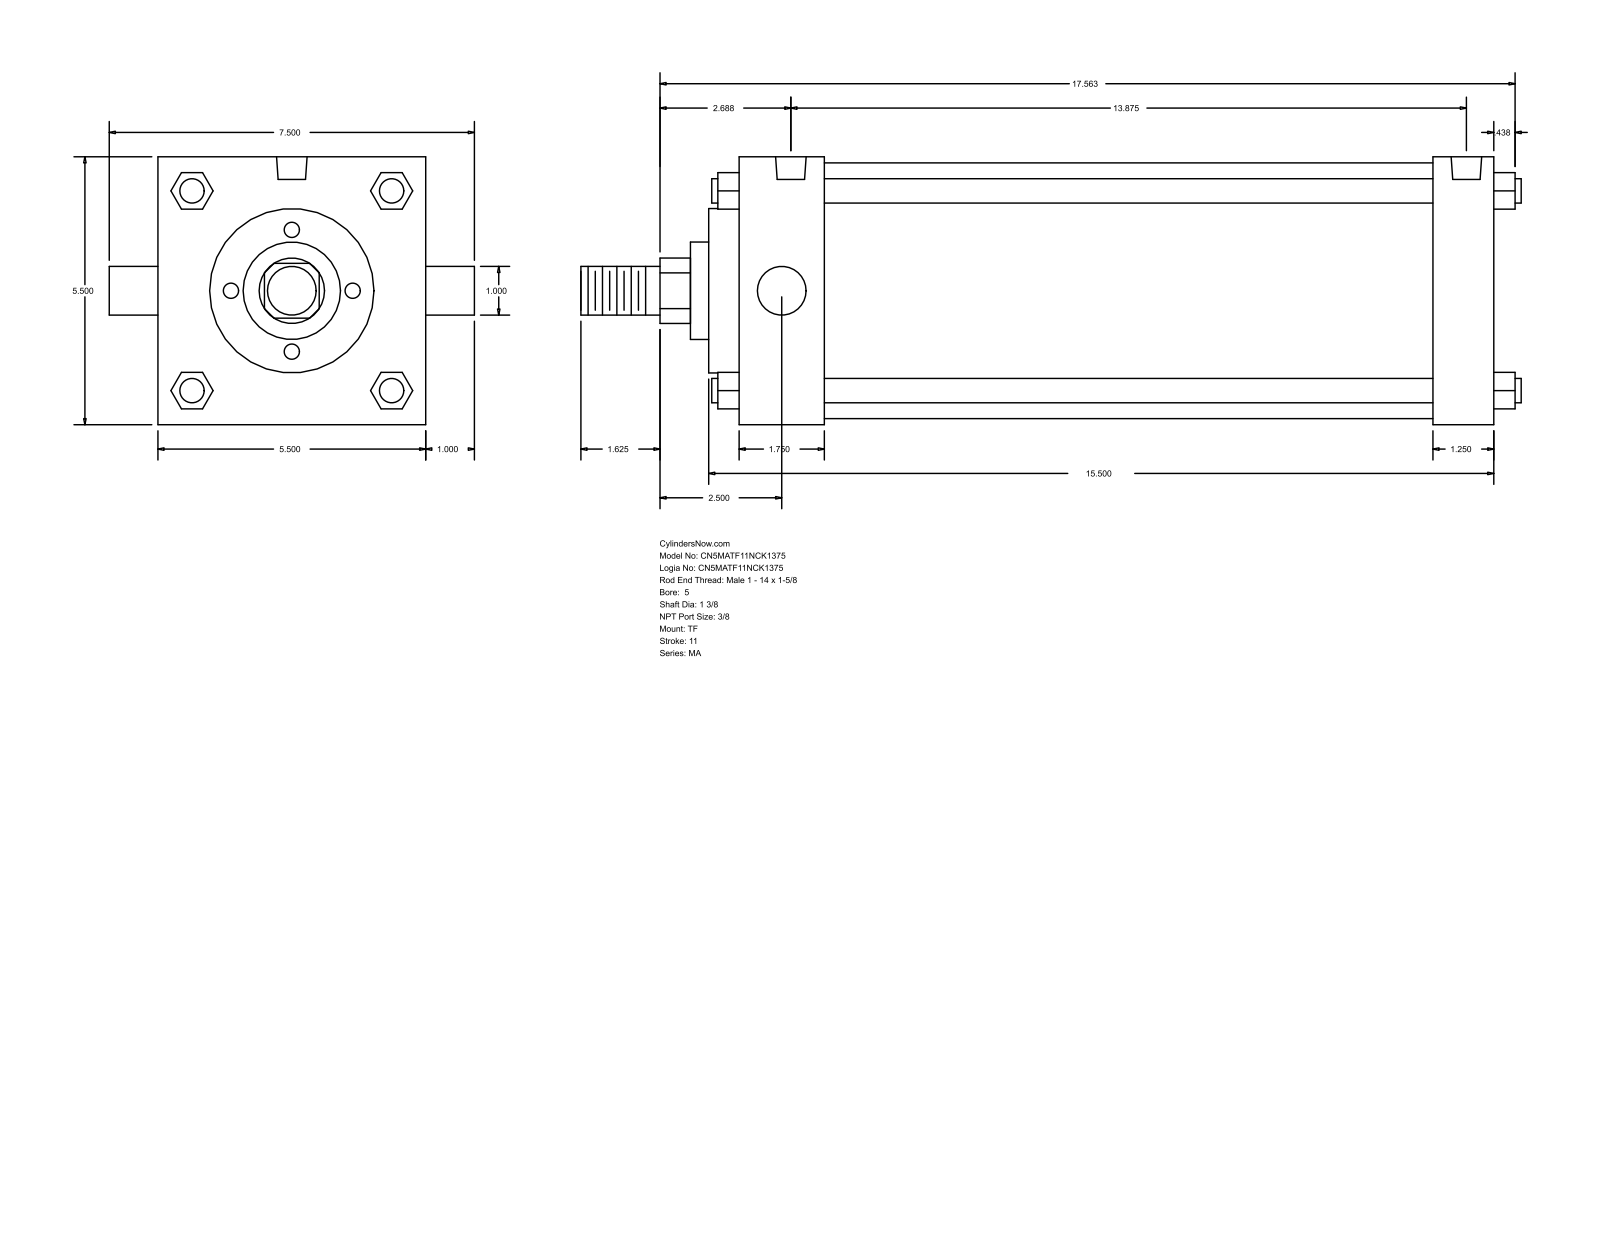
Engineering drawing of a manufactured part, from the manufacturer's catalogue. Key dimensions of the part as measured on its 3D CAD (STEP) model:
Part name (STEP PRODUCT): MA_TF__0500_1.375
STEP written by: GSSL Pune (CONFIG_CONTROL_DESIGN)
Units: millimetres
Bodies: 0 solids, 122 faces (93 planar, 29 cylindrical, 0 other)
Overall size (bounding box): 490.54 × 190.5 × 139.7
Round holes (diameter × count): ⌀11.11 ×3, ⌀15.93 ×2
Round bosses / shafts (diameter × count): ⌀12.7 ×4, ⌀25.4 ×2, ⌀133.35 ×1, ⌀85.72 ×1, ⌀50.8 ×1, ⌀34.92 ×1
Partial cylindrical surfaces — rounded edges, fillets, slot ends (radius × count): R17.06 ×1
Main face-to-face distances: 139.7, 393.71, 361.96, 31.75, 44.45, 317.51, 349.26, 15.87, 60.32, 377.83
Hole centre spacings: 4.76, 4.77, 342.9, 347.66, 347.67, 352.43
